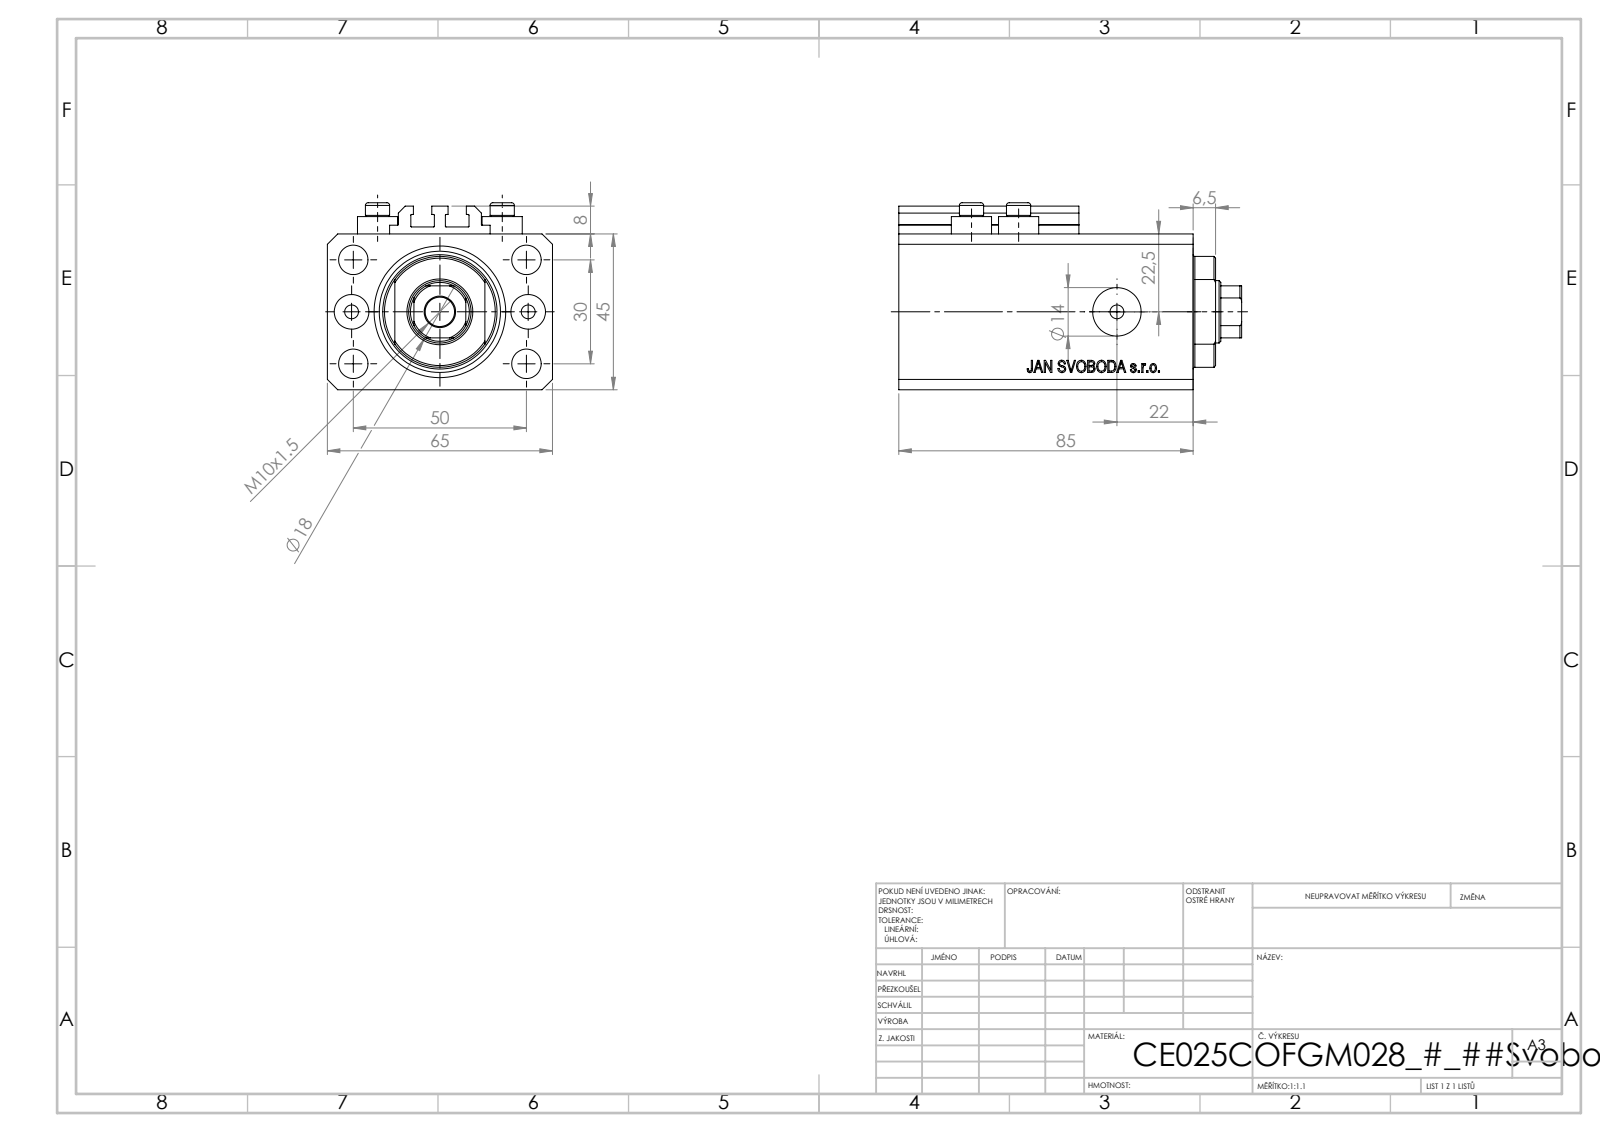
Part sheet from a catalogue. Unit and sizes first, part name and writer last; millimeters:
Units: millimetres
Overall size (bounding box): 99 × 65 × 54
Round holes (diameter × count): ⌀4 ×8, ⌀8.5 ×5, ⌀10 ×2, ⌀14 ×2, ⌀18 ×1, ⌀25 ×1, ⌀38 ×1
Round bosses / shafts (diameter × count): ⌀11.6 ×4, ⌀7 ×4
Partial cylindrical surfaces — rounded edges, fillets, slot ends (radius × count): R0.2 ×10, R8.5 ×1, R16 ×1
Main face-to-face distances: 45, 65, 14, 71, 85, 47, 6.9, 64.1, 78.1, 3
Hole centre spacings: 15.01, 29.15, 52.68, 13.6, 25.5, 30, 36, 38.48
Volume: 232 497 mm³ · Surface area: 61 711 mm²
Bodies: 8 solids, 1034 faces (504 planar, 86 cylindrical, 444 other)
Part name (STEP PRODUCT): ALLEN BOLT V250CE; V250CE_C_VCP; V250CE_VC_C; V250CE_C_Body
STEP written by: SolidWorks 2019 (CONFIG_CONTROL_DESIGN)
